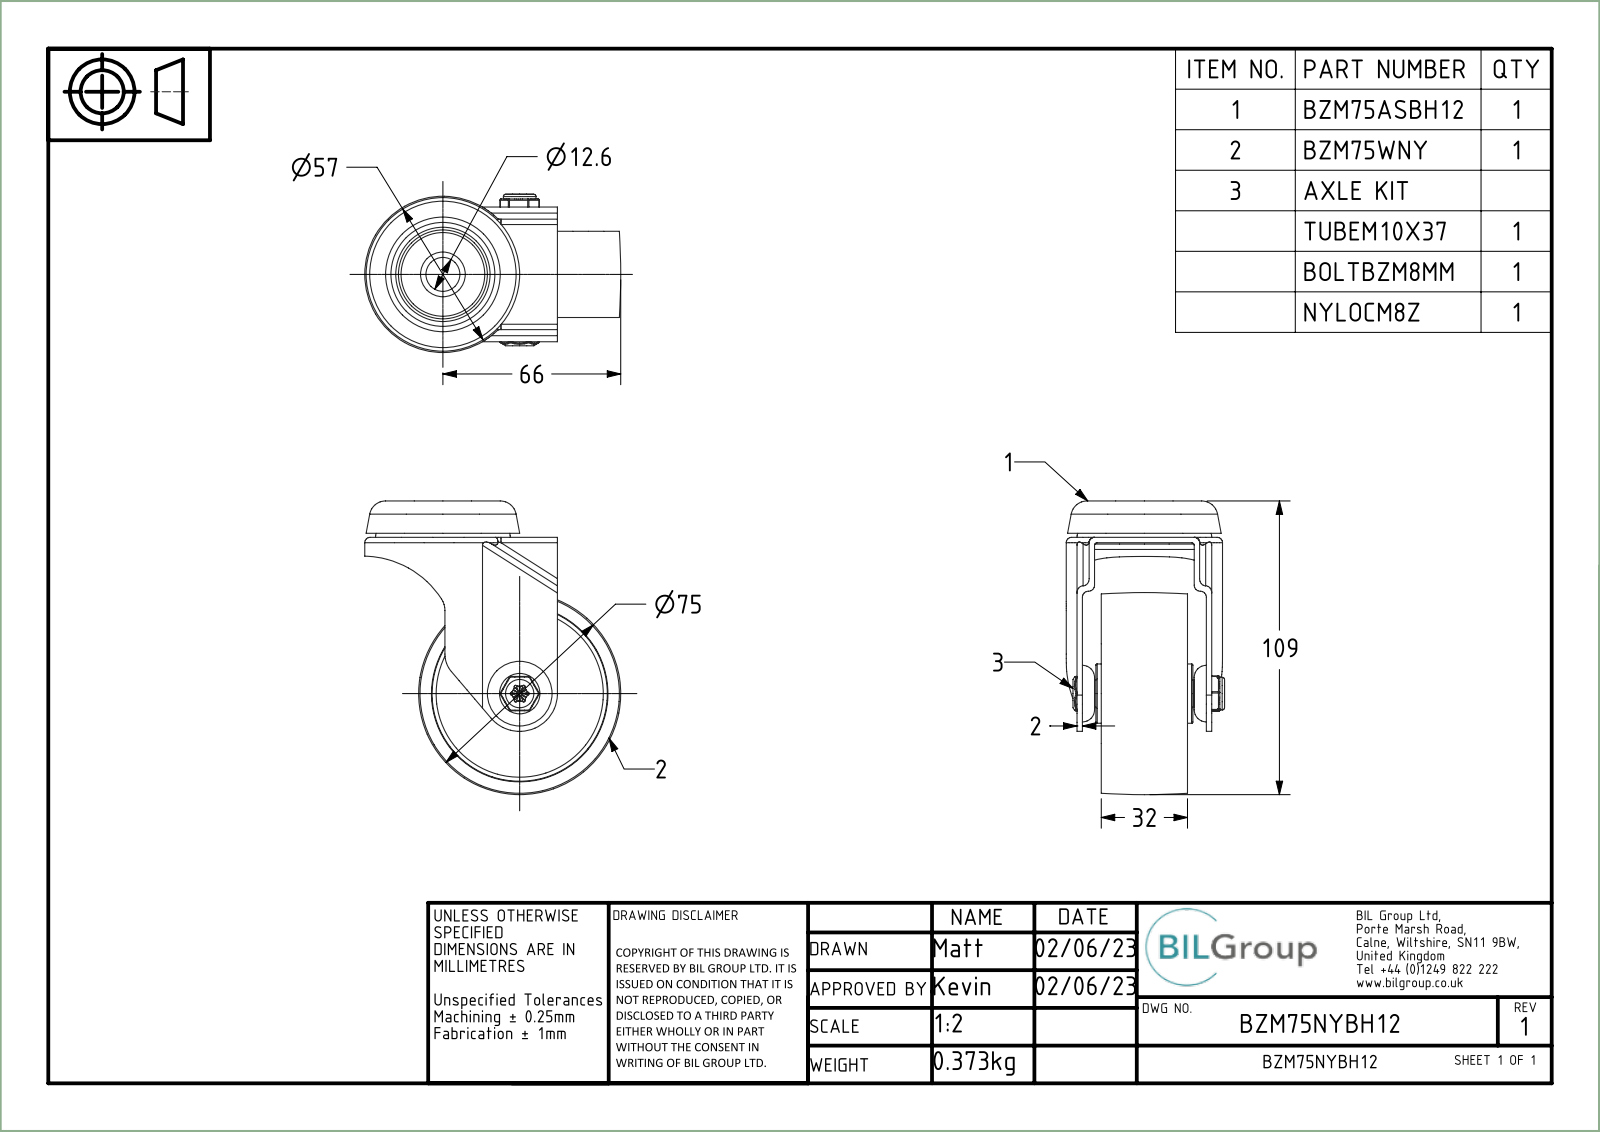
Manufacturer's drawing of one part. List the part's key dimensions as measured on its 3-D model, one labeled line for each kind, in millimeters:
Part name (STEP PRODUCT): BZM75ASBH12; ZINC PLATED PRESSED STEEL HEAD; ZINC PLATED PRESSED STEEL FORKS; BZM75NYBH12 (+8 more)
STEP written by: Spatial InterOp 3D (CONFIG_CONTROL_DESIGN)
Units: millimetres
Bodies: 7 solids, 364 faces (66 planar, 164 cylindrical, 134 other)
Overall size (bounding box): 109 × 95 × 58.75
Volume: 99 490 mm³ · Surface area: 61 009 mm²
Round holes (diameter × count): ⌀8 ×1, ⌀8.2 ×1, ⌀8.3 ×1, ⌀8.6 ×1, ⌀10.2 ×1, ⌀12.6 ×1, ⌀30 ×1
Round bosses / shafts (diameter × count): ⌀48 ×1, ⌀22 ×1, ⌀12.1 ×1, ⌀10 ×1, ⌀6 ×1
Partial cylindrical surfaces — rounded edges, fillets, slot ends (radius × count): R0.5 ×30, R2 ×14, R2.25 ×8, R1 ×2, R2.75 ×1, R8 ×1, R10 ×1, R14 ×1
Main face-to-face distances: 2, 4, 41, 2.5, 4.5, 39, 7, 27, 23, 18
